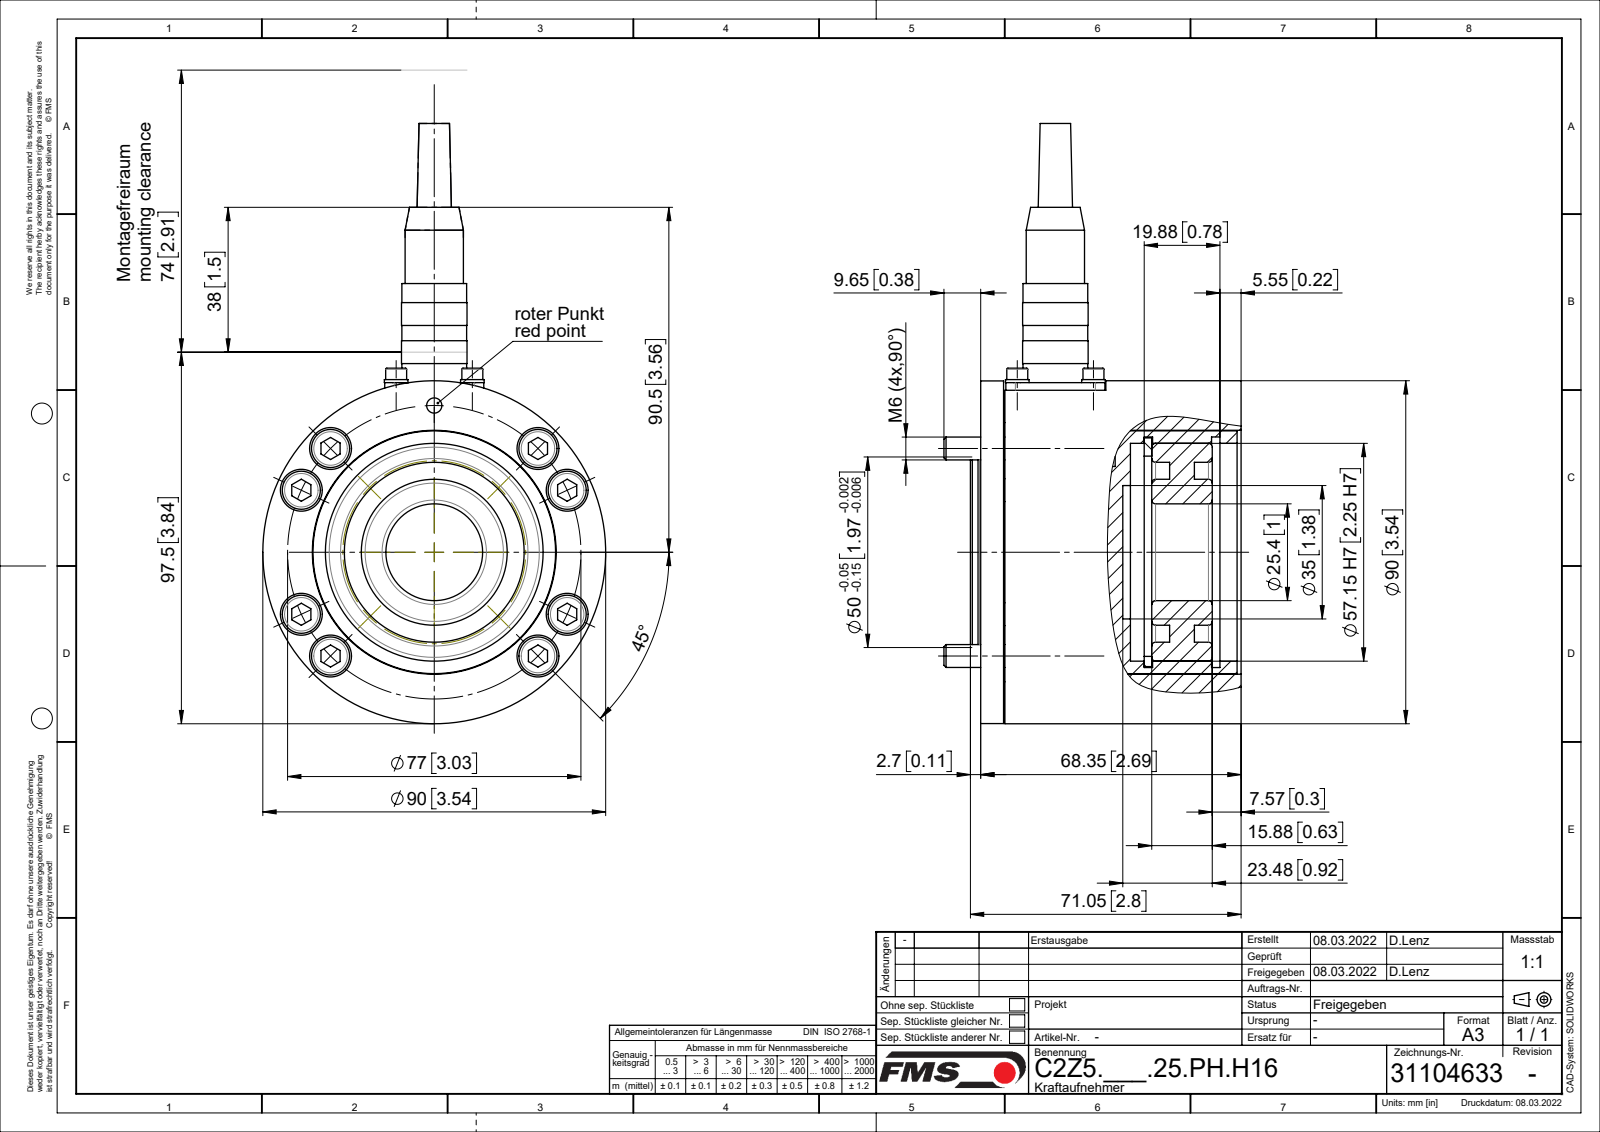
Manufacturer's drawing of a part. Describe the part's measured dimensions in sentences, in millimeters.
The part is named "Flanschstecker_M14x1_Mini_5pol; 31104488_01; 31104502_01; 31104498_stp_nach_Vergueten (+8 more)". Its 3-D file was written by "SolidWorks 2018 (CONFIG_CONTROL_DESIGN)". It is 23 solids with 578 faces: 206 planar, 258 cylindrical and 114 other. Overall it measures 157.5 by 90 by 78 millimeters. Its volume is 304 979 cubic millimeters and its surface area 121 027 square millimeters. Round holes: 8 of diameter 6.5, 8 of diameter 11, 6 of diameter 2.5, 4 of diameter 3.1, 4 of diameter 3.2, 4 of diameter 5, 4 of diameter 7, 2 of diameter 4, 1 of diameter 10.2, 1 of diameter 12, 1 of diameter 15, 1 of diameter 18. Round bosses or shafts: 8 of diameter 10, 8 of diameter 6, 5 of diameter 1.5, 4 of diameter 6.2, 4 of diameter 5.5, 4 of diameter 3, 1 of diameter 90, 1 of diameter 89.9. Partial cylindrical surfaces (rounded edges, fillets, slot ends): 4 of radius 0.1, 4 of radius 2.5, 2 of radius 4.16, 2 of radius 5, 1 of radius 23.2, 1 of radius 26.29. The main face-to-face distances are 6, 3.3, 2.7, 33.05, 32, 2, 38, 30, 29.3, 35.3. The hole center spacings are 20, 38.5, 13.37, 14.14, 38.49, 44.16, 54.44, 63.07.
